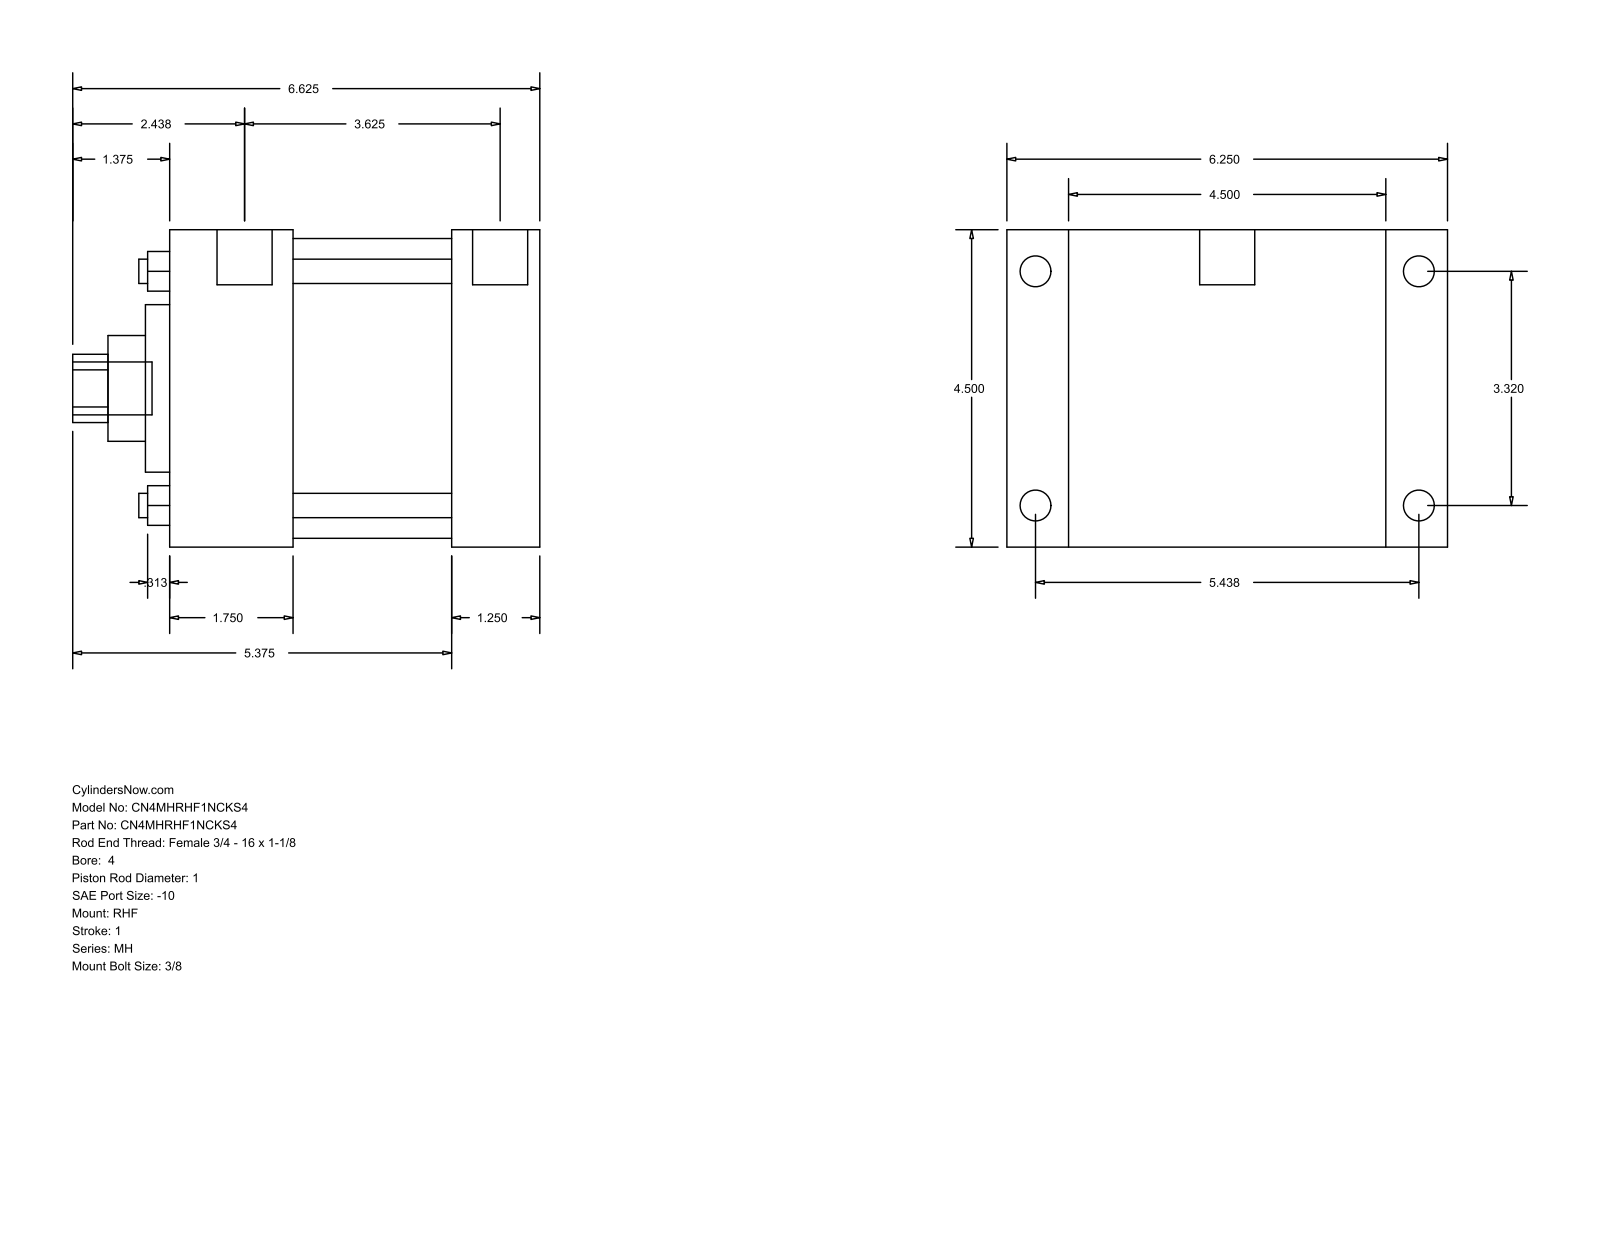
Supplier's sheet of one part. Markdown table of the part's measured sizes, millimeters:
| quantity | value |
| --- | --- |
| part name | MH_RHF__0400_1 |
| STEP written by | GSSL Pune (CONFIG_CONTROL_DESIGN) |
| units | millimeters |
| bodies | 0 solids, 90 faces (61 planar, 29 cylindrical, 0 other) |
| overall size | 168.28 × 158.75 × 114.3 |
| round holes (diameter × count) | 8.76 × 4, 25.4 × 1, 38.1 × 1, 60.33 × 1, 107.95 × 1 |
| round bosses / shafts (diameter × count) | 11.13 × 4, 8.73 × 4, 19.84 × 2, 19.05 × 1 |
| partial cylindrical surfaces (radius × count) | 12.29 × 1 |
| main face-to-face distances | 114.3, 133.36, 101.61, 31.75, 136.53, 22.23, 44.46, 57.15, 88.9, 158.76 |
| hole center spacings | 59.62, 84.32, 119.25 |
